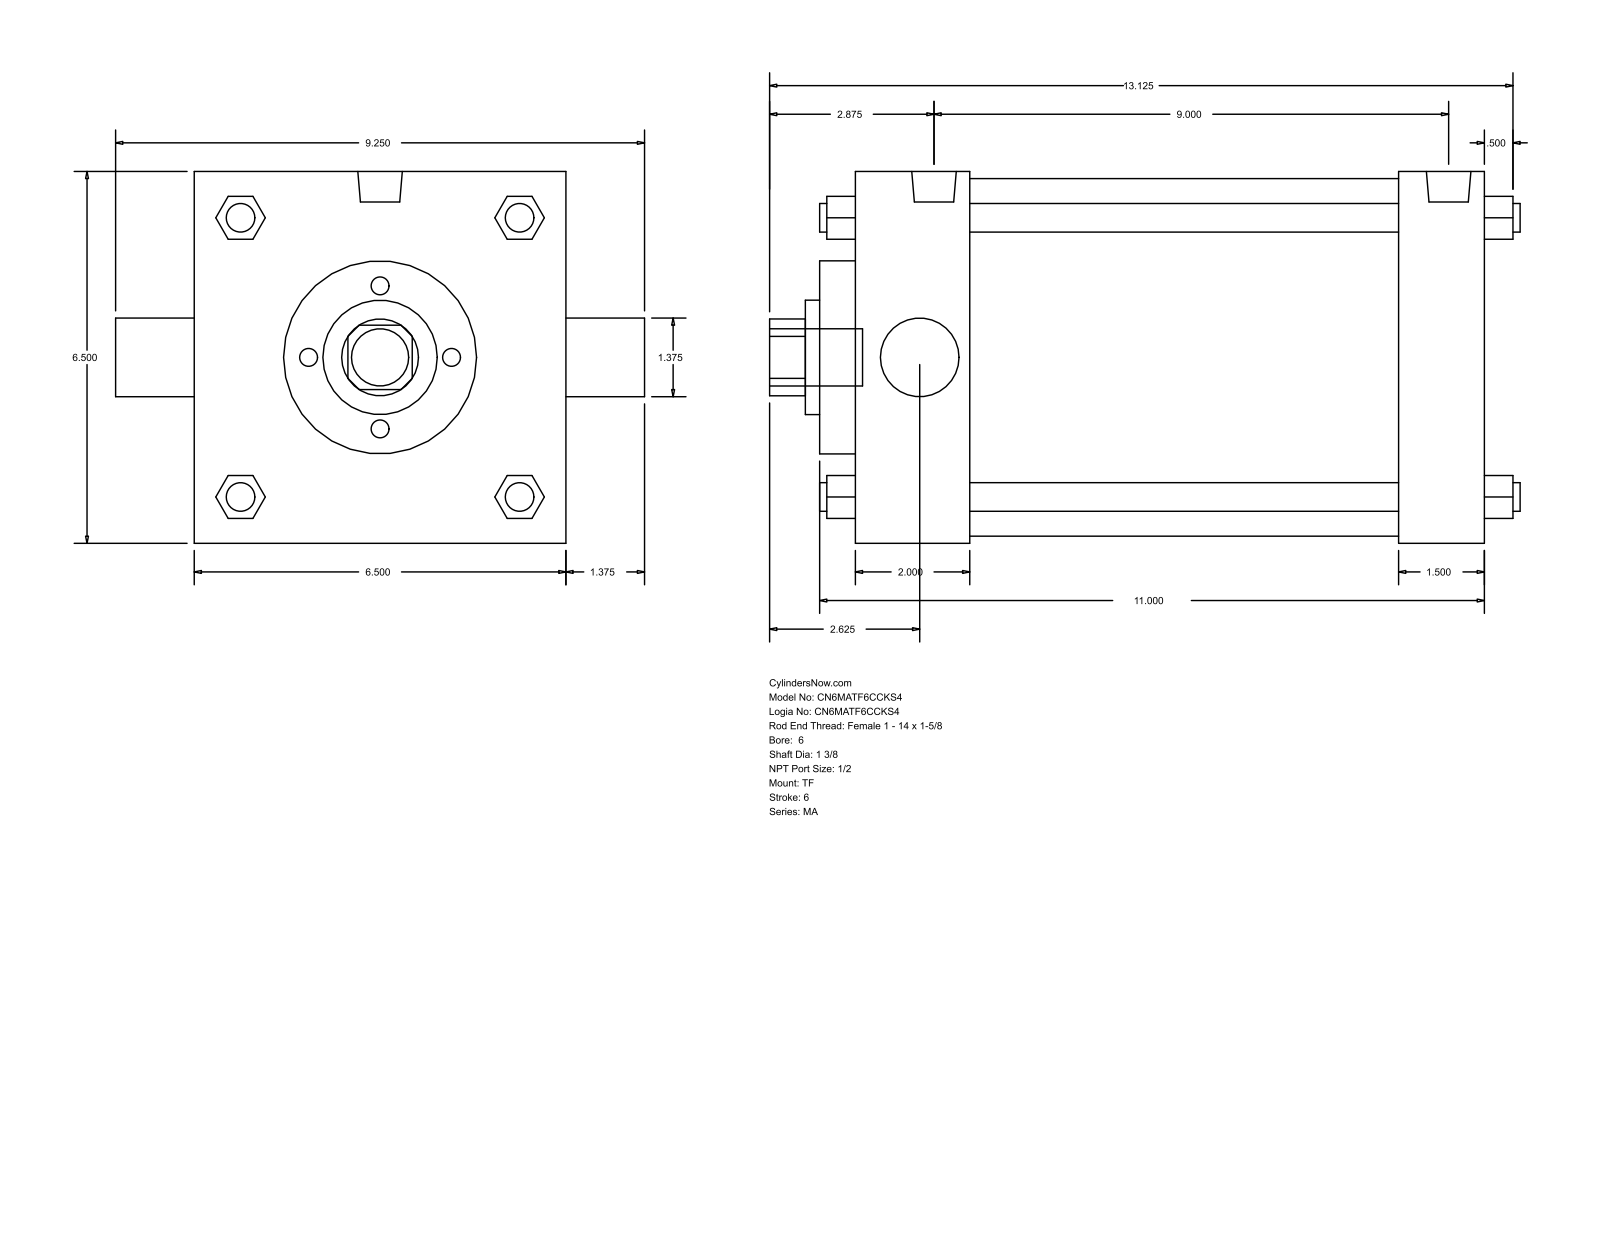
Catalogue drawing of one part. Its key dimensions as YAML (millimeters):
part_name: "MA_TF__0600_1.375"
step_written_by: "GSSL Pune (CONFIG_CONTROL_DESIGN)"
units: millimeters
bodies: {solids: 0, faces: 122, planar: 93, cylindrical: 29, other: 0}
overall_size: [333.38, 234.95, 165.1]
round_holes:
  - {diameter: 34.92, count: 2}
  - {diameter: 50.8, count: 1}
  - {diameter: 85.72, count: 1}
  - {diameter: 158.75, count: 1}
round_bosses_or_shafts:
  - {diameter: 12.7, count: 4}
  - {diameter: 17.46, count: 3}
  - {diameter: 19.77, count: 2}
  - {diameter: 25.4, count: 1}
partial_cylinders:
  - {radius: 17.06, count: 1}
face_to_face_distances: [165.1, 282.58, 50.8, 231.78, 244.47, 193.67, 38.11, 15.87, 66.67, 260.34]
